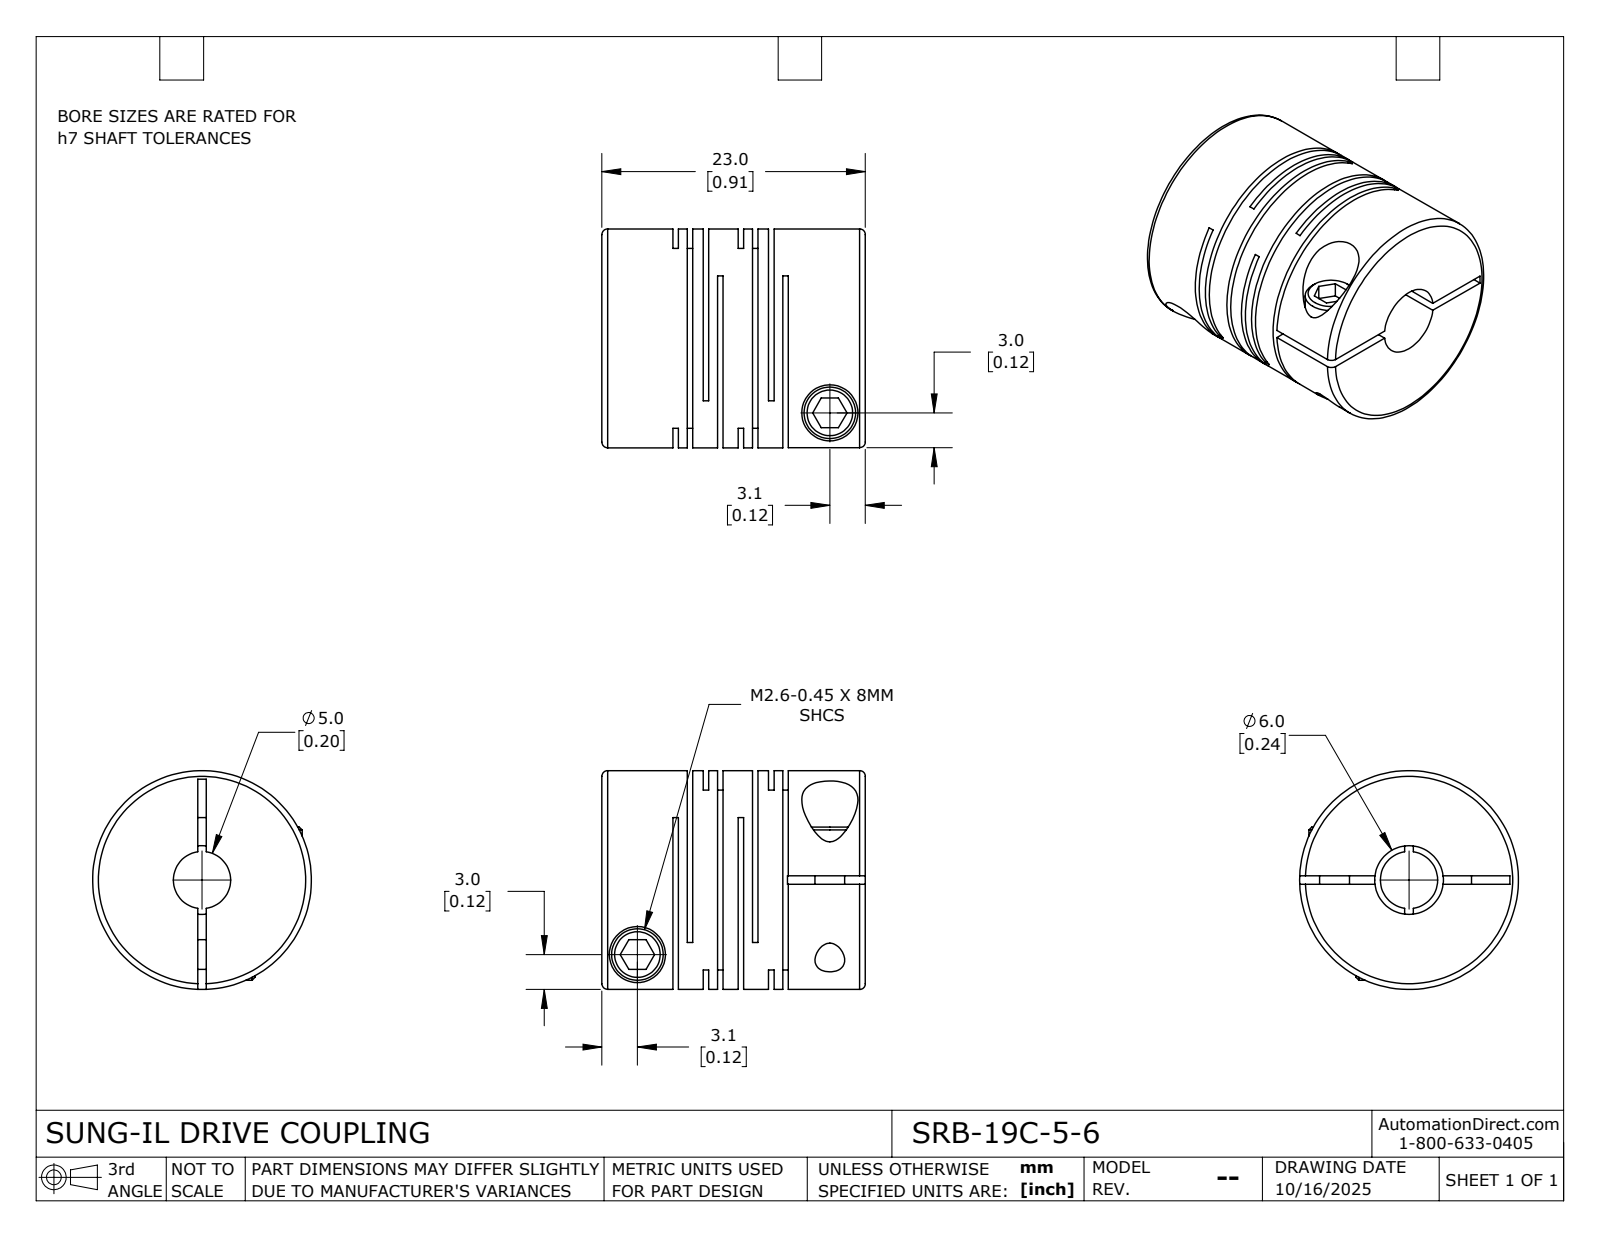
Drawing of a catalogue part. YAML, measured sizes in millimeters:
part_name: "SRB-19C-5-6"
step_written_by: "SolidWorks 2024 (CONFIG_CONTROL_DESIGN)"
units: millimeters
bodies: {solids: 1, faces: 115, planar: 60, cylindrical: 42, other: 13}
overall_size: [23, 19.1, 19.1]
volume: 4927
surface_area: 6023
round_holes:
  - {diameter: 2.6, count: 2}
  - {diameter: 4.9, count: 2}
  - {diameter: 5, count: 1}
  - {diameter: 6, count: 1}
round_bosses_or_shafts:
  - {diameter: 4.5, count: 2}
  - {diameter: 19.1, count: 1}
face_to_face_distances: [2.65, 5.7, 0.48, 1.25, 2.17, 3.05, 5.22, 0.77, 4.45, 1.4]
